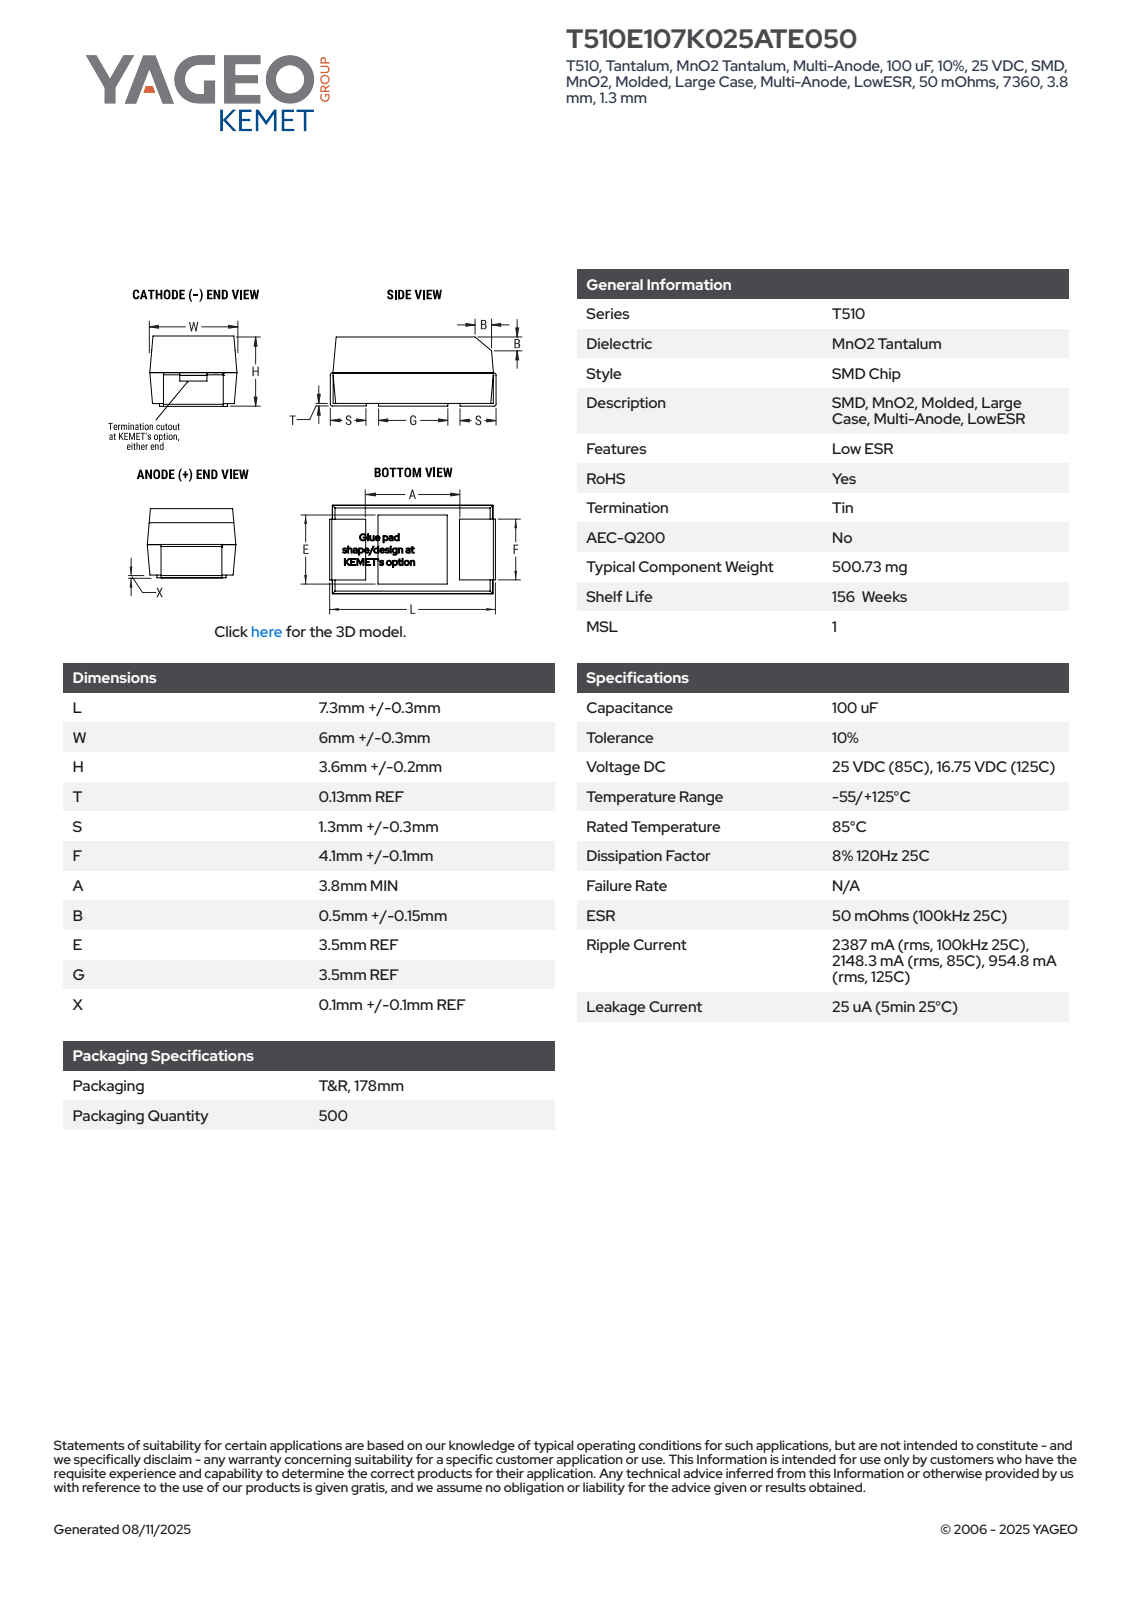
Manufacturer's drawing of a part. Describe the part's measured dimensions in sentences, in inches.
The part is named "CTSM_TCM2NKRP_7360_L7.6W6.3H3.8T0.13S1.3F4.2A3.8B0.65E3.5G3.5X0.2". Its 3-D file was written by "SolidWorks 2014 (AUTOMOTIVE_DESIGN)". It is 4 solids with 94 faces: 90 planar, 4 cylindrical and 0 other. Overall it measures 0.299 by 0.248 by 0.15 inches. Its volume is 0.01 cubic inches and its surface area 0.352 square inches. Partial cylindrical surfaces (rounded edges, fillets, slot ends): 4 of radius 0.004. The main face-to-face distances are 0.15, 0.142, 0.294, 0.244, 0.244, 0.144, 0.299, 0.289, 0.081, 0.219.
